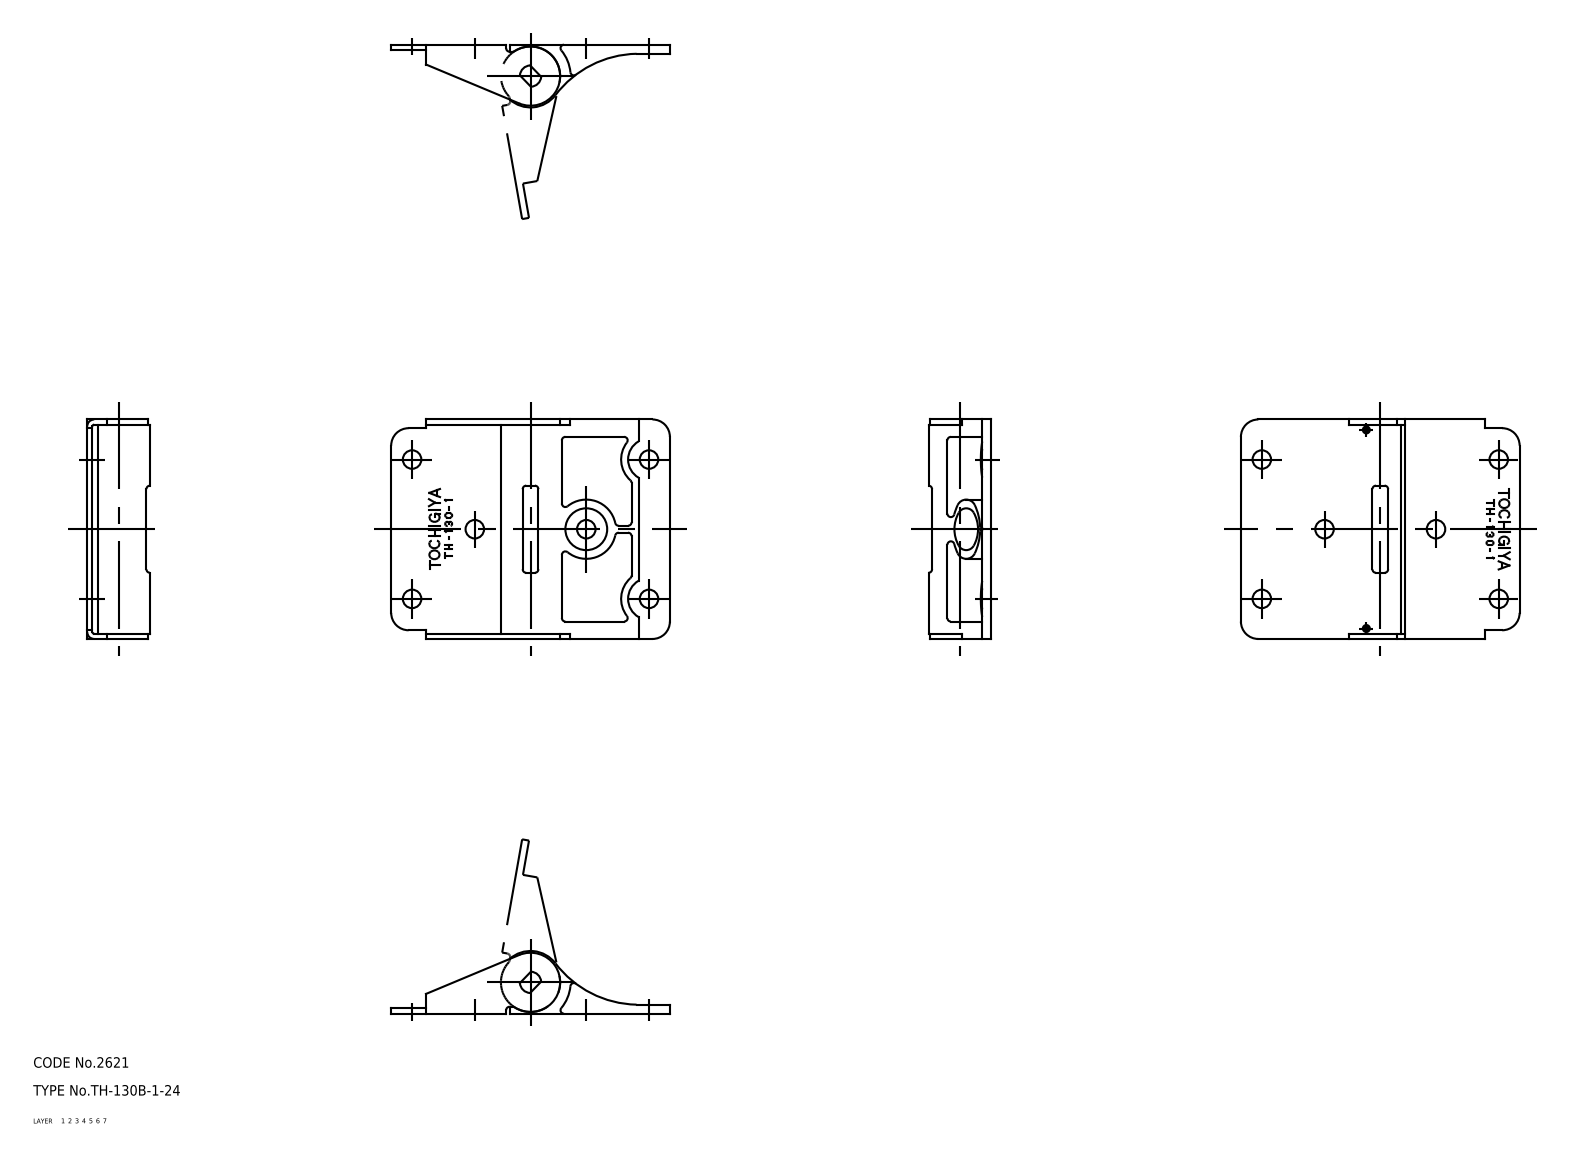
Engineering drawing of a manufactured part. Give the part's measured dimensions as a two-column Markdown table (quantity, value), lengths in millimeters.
| quantity | value |
| --- | --- |
| part name | shaft; hinge piece; TH_130B_1_24_3550_36 |
| STEP written by | CADfix (AUTOMOTIVE_DESIGN) |
| units | millimeters |
| bodies | 3 solids, 117 faces (0 planar, 0 cylindrical, 117 other) |
| overall size | 80 × 63 × 18 |
| volume | 26 390 mm³ |
| surface area | 17 160 mm² |
